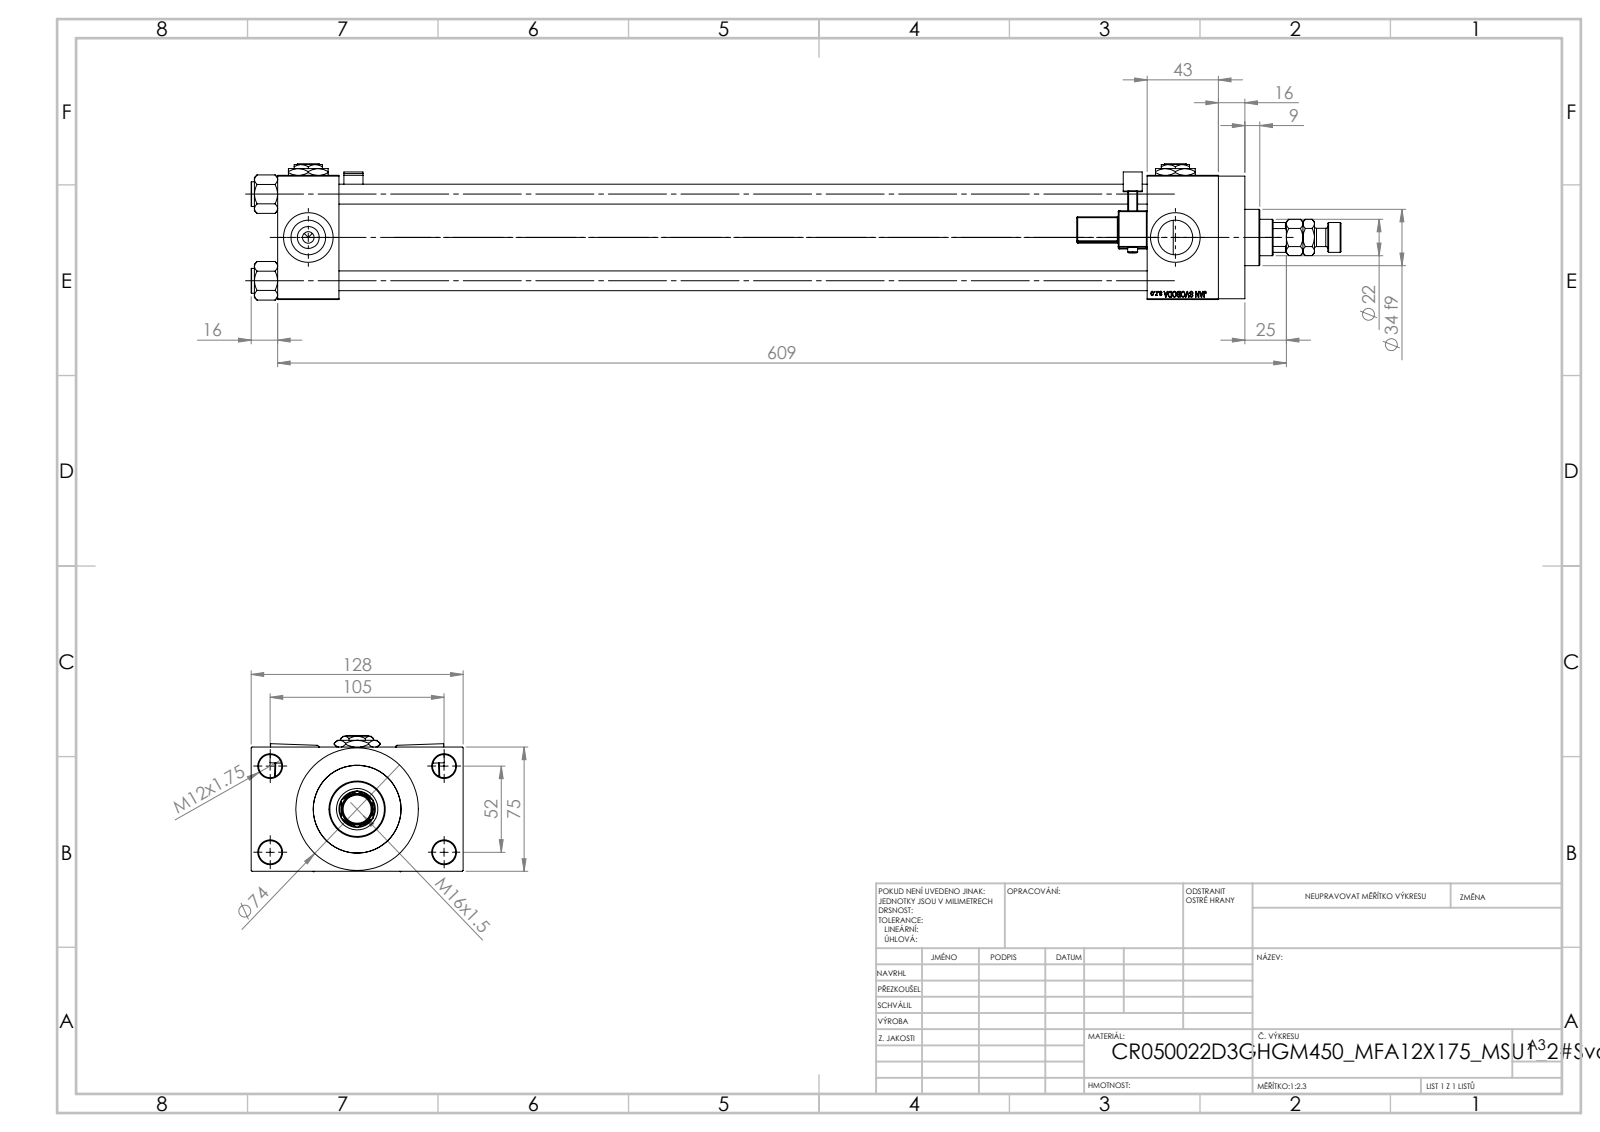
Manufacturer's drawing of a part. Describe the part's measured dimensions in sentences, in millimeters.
The part is named "NUT_M5_D; Zatka_pro_OIL_PORT; V215CR_VCP_D; V215CR_MSU (+4 more)". Its 3-D file was written by "SolidWorks 2019 (CONFIG_CONTROL_DESIGN)". It is 16 solids with 1410 faces: 619 planar, 163 cylindrical and 628 other. Overall it measures 658 by 128 by 82.27 millimeters. Its volume is 1 415 000 cubic millimeters and its surface area 423 643 square millimeters. Round holes: 4 of diameter 12, 4 of diameter 14, 4 of diameter 20.96, 4 of diameter 30, 3 of diameter 7, 1 of diameter 10.5, 1 of diameter 22, 1 of diameter 25, 1 of diameter 41, 1 of diameter 50, 1 of diameter 53. Round bosses or shafts: 4 of diameter 15, 2 of diameter 6, 1 of diameter 74, 1 of diameter 56, 1 of diameter 34, 1 of diameter 18, 1 of diameter 11. Partial cylindrical surfaces (rounded edges, fillets, slot ends): 48 of radius 0.5, 2 of radius 1, 2 of radius 2.5, 2 of radius 4, 1 of radius 10.5. The main face-to-face distances are 75, 488, 37, 525, 26.5, 101.5, 568, 531, 43, 16. The hole center spacings are 26.35, 36.98, 52.3, 58.43, 58.59, 78.65, 94.37, 52.
